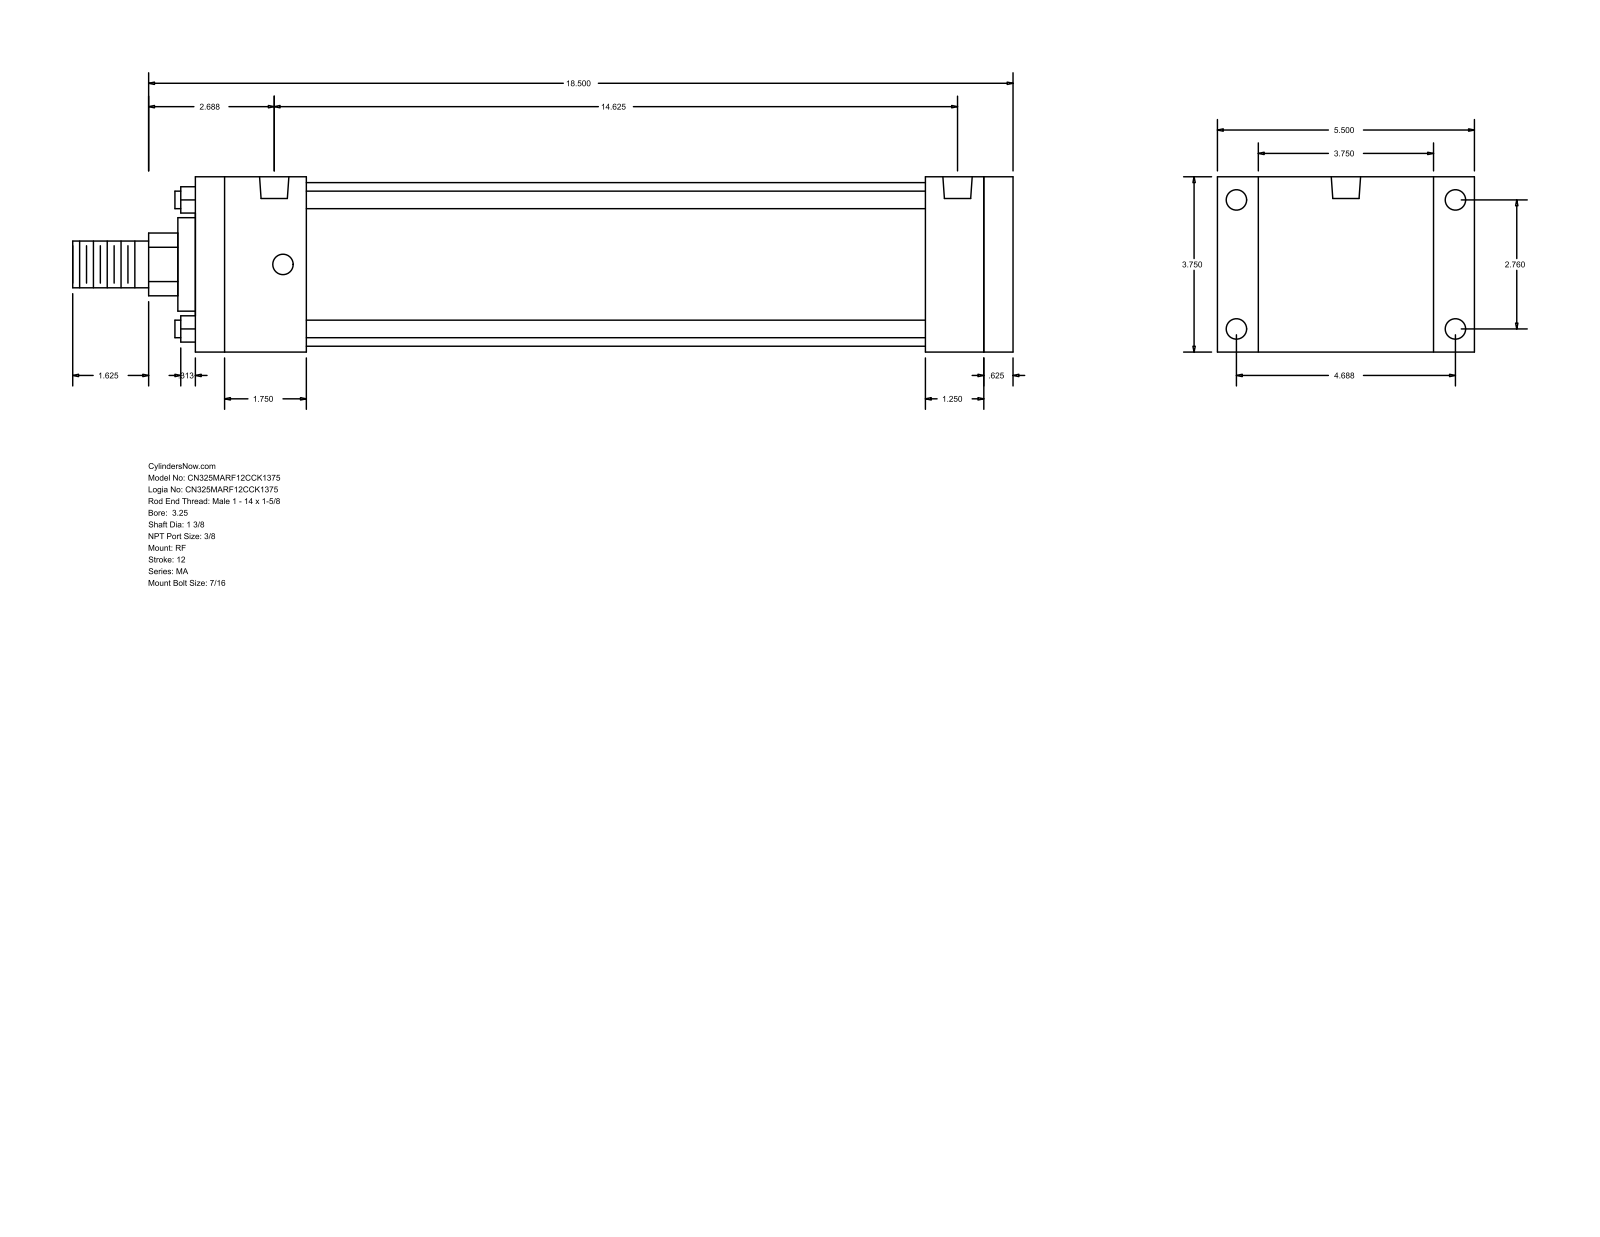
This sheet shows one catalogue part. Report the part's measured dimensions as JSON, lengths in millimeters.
{"part_name": "MA_RF__0325_1.375", "step_written_by": "GSSL Pune (CONFIG_CONTROL_DESIGN)", "units": "millimeters", "bodies": {"solids": 0, "faces": 92, "planar": 64, "cylindrical": 28, "other": 0}, "overall_size": [511.18, 139.7, 95.25], "round_holes": [[11.11, 8], [15.93, 2]], "round_bosses_or_shafts": [[9.53, 4], [88.9, 1], [50.8, 1], [34.92, 1], [25.4, 1]], "partial_cylinders_radius": [[17.06, 1]], "face_to_face_distances": [95.24, 444.5, 15.88, 428.62, 22.23, 117.47, 396.87, 31.75, 47.63, 60.32], "hole_center_spacings": [70.1, 119.06, 138.16, 361.95, 4.76, 4.77, 366.71, 366.72]}
